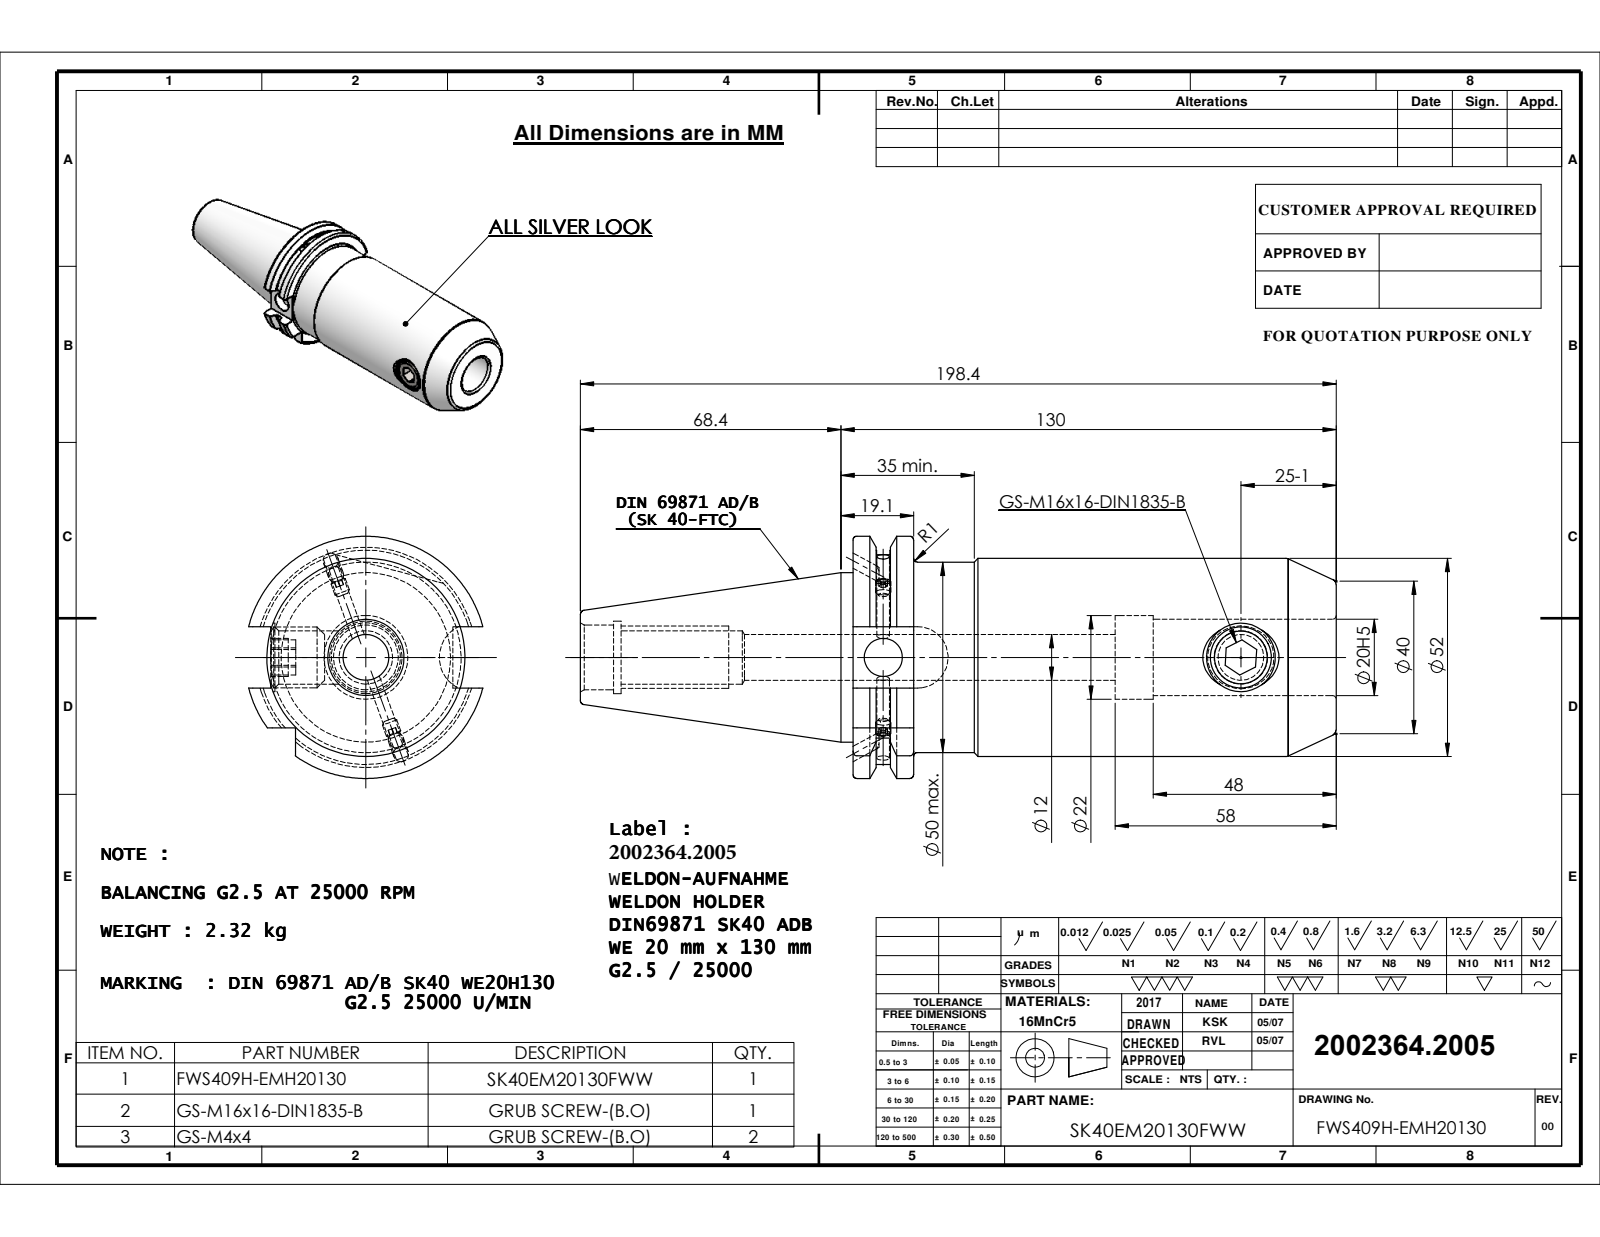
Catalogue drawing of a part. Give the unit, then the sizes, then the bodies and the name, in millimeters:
Units: millimetres
Overall size (bounding box): 198.4 × 63.55 × 61.48
Round holes (diameter × count): ⌀14 ×2, ⌀3.3 ×1, ⌀10 ×1, ⌀12 ×1, ⌀17 ×1, ⌀18 ×1, ⌀19 ×1, ⌀20 ×1, ⌀22 ×1
Round bosses / shafts (diameter × count): ⌀4 ×2, ⌀52 ×1, ⌀50 ×1, ⌀44.45 ×1, ⌀16 ×1
Partial cylindrical surfaces — rounded edges, fillets, slot ends (radius × count): R8.05 ×1, R28.12 ×1, R31.77 ×1
Main face-to-face distances: 126.8, 15.9, 110.9, 68.8, 52.9, 58, 16.1, 47.8, 71.6, 87.5
Hole centre spacings: 93.85
Volume: 300 948 mm³ · Surface area: 46 025 mm²
Bodies: 4 solids, 167 faces (59 planar, 47 cylindrical, 61 other)
Part name (STEP PRODUCT): 91406-WE720130; SK40EM20130FWW; Copy of M4X4_DIN 913 - M4 x 4-N; M16X16_ISO 4026 - M16 x 10-N
STEP written by: SolidWorks 2009 (CONFIG_CONTROL_DESIGN)
